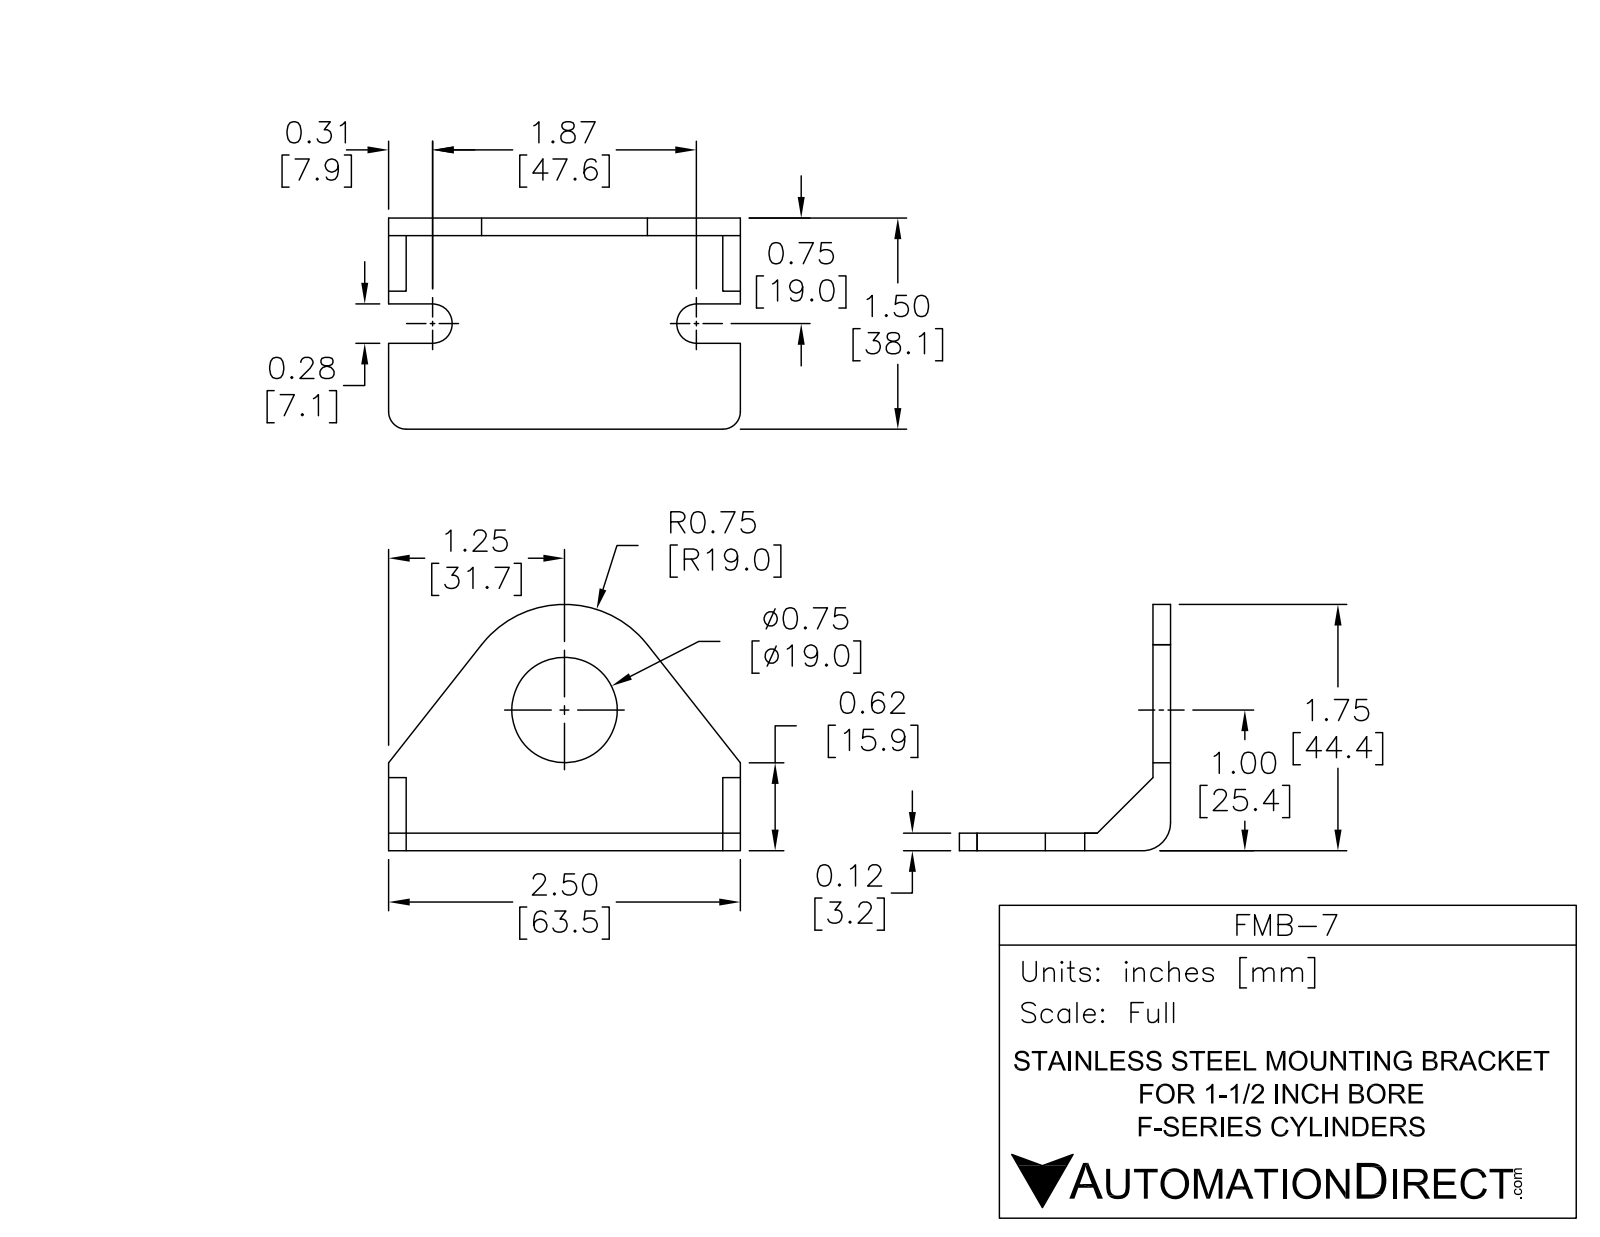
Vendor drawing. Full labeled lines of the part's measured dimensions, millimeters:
Part name (STEP PRODUCT): FMB-7
STEP written by: SolidWorks 2017 (AUTOMOTIVE_DESIGN)
Units: millimetres
Bodies: 1 solid, 28 faces (19 planar, 9 cylindrical, 0 other)
Overall size (bounding box): 63.5 × 44.5 × 38.1
Volume: 12 500 mm³ · Surface area: 9 006 mm²
Round holes (diameter × count): ⌀19.1 ×1
Partial cylindrical surfaces — rounded edges, fillets, slot ends (radius × count): R3.6 ×2, R4.7 ×2, R1.5 ×1, R4.7 ×1, R19.1 ×1
Main face-to-face distances: 3.2, 3.2, 63.5, 34.9, 38.1, 2.5, 61, 15.5, 22.6, 58.4
